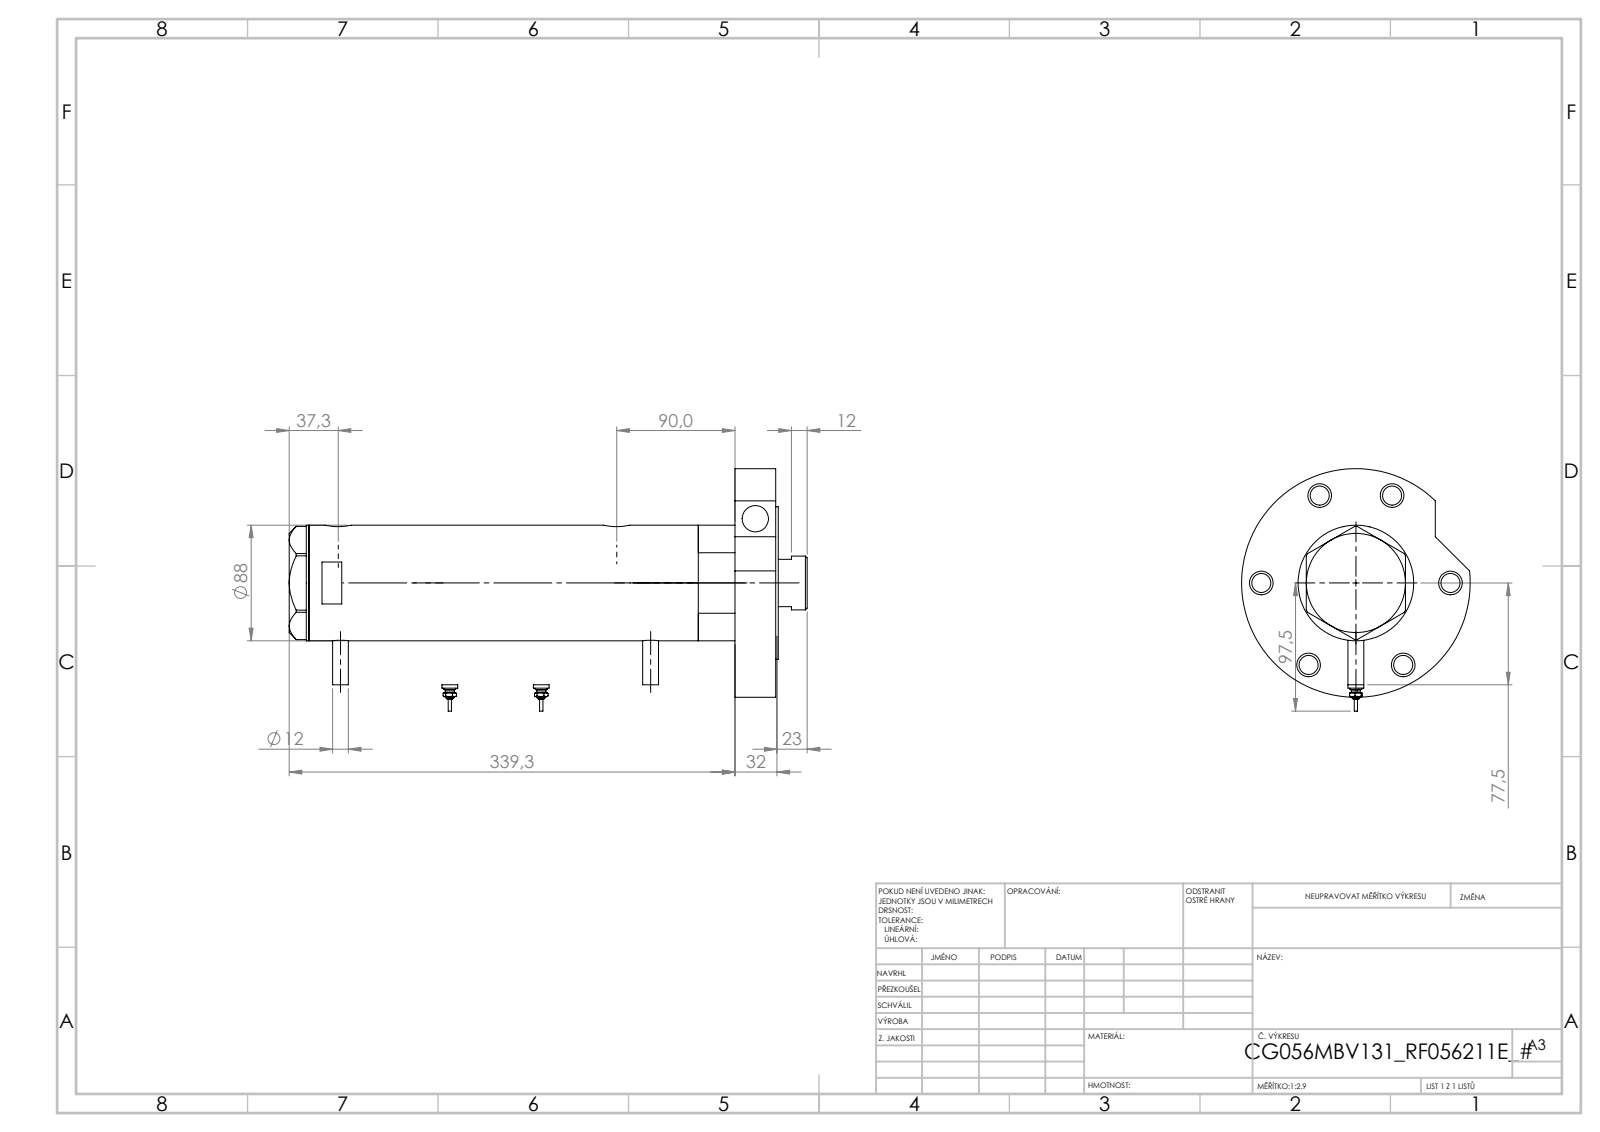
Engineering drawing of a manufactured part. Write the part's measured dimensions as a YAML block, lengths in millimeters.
part_name: "V270CG_VC; V270CG_BACK; V270CG_FRONT; V270CG_RF211E (+2 more)"
step_written_by: "SolidWorks 2019 (CONFIG_CONTROL_DESIGN)"
units: millimeters
bodies: {solids: 7, faces: 257, planar: 91, cylindrical: 102, other: 64}
overall_size: [394.3, 184.5, 174]
volume: 2581000
surface_area: 361527
round_holes:
  - {diameter: 14.5, count: 7}
  - {diameter: 18, count: 6}
  - {diameter: 20, count: 3}
  - {diameter: 12.5, count: 2}
  - {diameter: 13.16, count: 2}
  - {diameter: 42, count: 1}
  - {diameter: 43.5, count: 1}
  - {diameter: 56, count: 1}
  - {diameter: 60, count: 1}
  - {diameter: 75, count: 1}
  - {diameter: 80, count: 1}
round_bosses_or_shafts:
  - {diameter: 12, count: 4}
  - {diameter: 9, count: 2}
  - {diameter: 7, count: 2}
  - {diameter: 4.5, count: 2}
  - {diameter: 2.5, count: 2}
  - {diameter: 174, count: 1}
  - {diameter: 116, count: 1}
  - {diameter: 88, count: 1}
face_to_face_distances: [31, 2, 357.3, 324.3, 355.3, 33, 234.4, 89.9, 120.9, 122.9]
hole_center_spacings: [72, 80, 119.73, 124.71, 129.15, 143.69, 1.7, 25.8]
